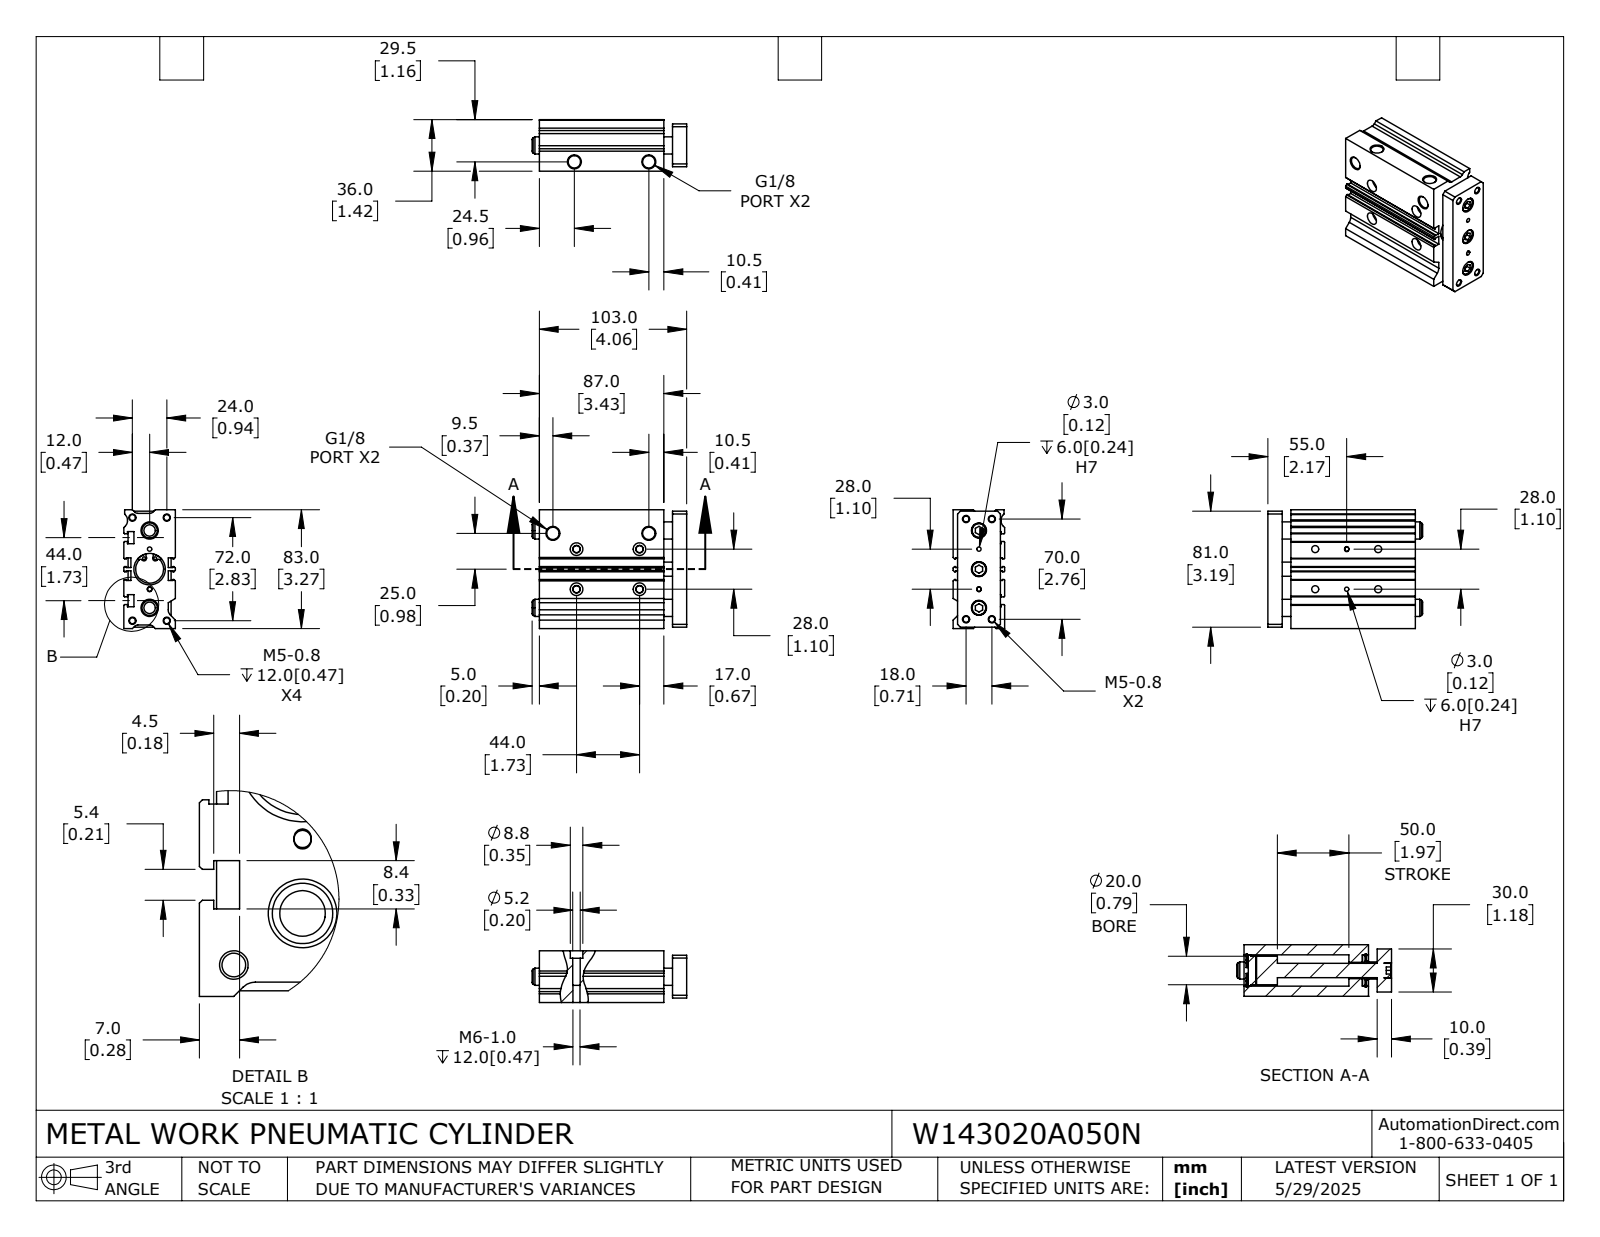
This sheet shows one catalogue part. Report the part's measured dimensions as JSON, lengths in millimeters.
{"part_name": "W143020A050N; W143020A050N_ROD; W143020A050N_BODY", "step_written_by": "SolidWorks 2024 (CONFIG_CONTROL_DESIGN)", "units": "millimeters", "bodies": {"solids": 6, "faces": 357, "planar": 174, "cylindrical": 145, "other": 38}, "overall_size": [108, 83, 36], "volume_mm3": 229300, "surface_area_mm2": 72190, "round_holes": [[4.1, 8], [2, 4], [3, 4], [5.2, 4], [8.6, 4], [8.8, 4], [10.5, 3], [4.9, 2], [4.9, 2], [12, 2], [11.4, 1], [19.5, 1]], "round_bosses_or_shafts": [[10, 3], [23, 2], [20, 1], [13, 1]], "partial_cylinders_radius": [[1.3, 4], [1.5, 4], [1.8, 4], [3, 4], [5, 3]], "face_to_face_distances": [36, 2.5, 5, 2, 31, 10, 6, 16, 26, 3], "hole_center_spacings": [3.1, 7.5, 8.5, 12, 15, 19.8, 21, 21.9]}
